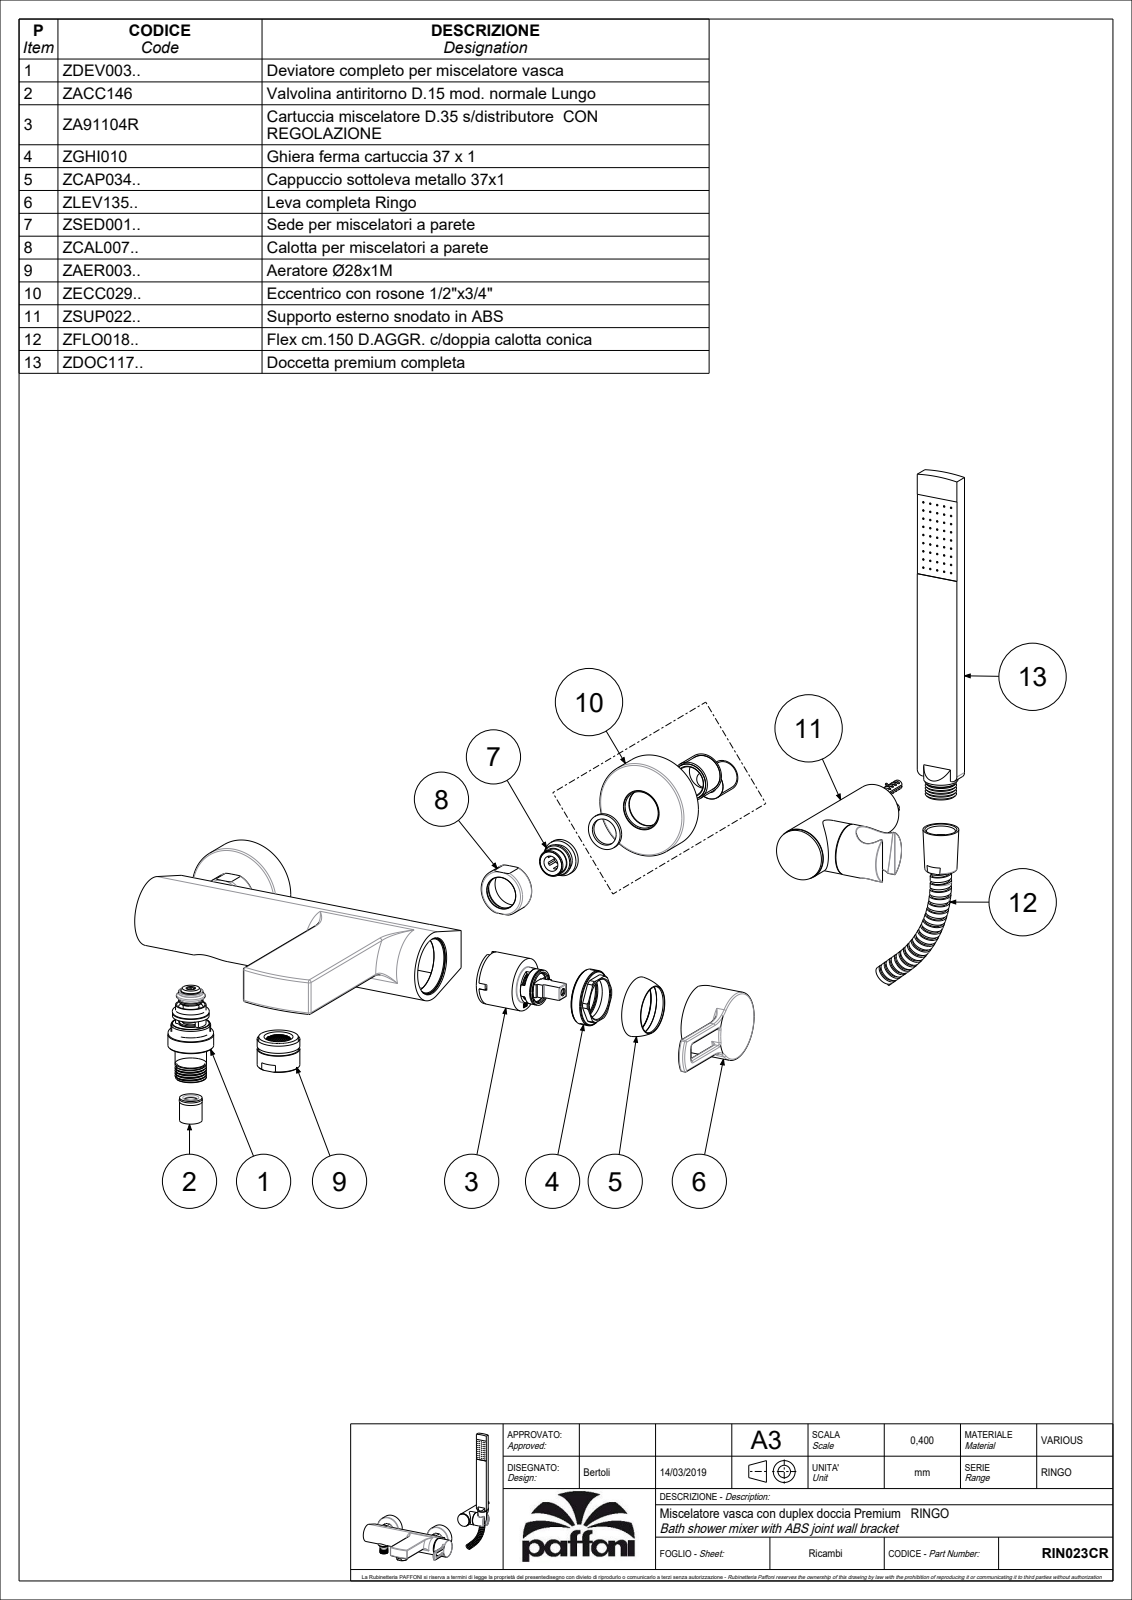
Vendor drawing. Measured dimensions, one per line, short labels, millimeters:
name: RIN023CR
written by: CREO PARAMETRIC BY PTC INC, 2020044 (CONFIG_CONTROL_DESIGN)
unit: mm
bodies: 7 solids, 3671 faces (2649 planar, 577 cylindrical, 445 other)
size: 385.7 × 364.5 × 195
volume: 468 678 mm³; area: 287 568 mm²
holes: 4× ⌀7, 3× ⌀20, 2× ⌀3.5, 2× ⌀4, 2× ⌀7.8, 2× ⌀9.5, 2× ⌀10.5, 2× ⌀12.7, 2× ⌀16, 2× ⌀18, 2× ⌀21, 2× ⌀21.6
bosses: 11× ⌀2, 3× ⌀27, 3× ⌀24, 3× ⌀6.9, 3× ⌀3.9, 2× ⌀63.5, 2× ⌀30, 2× ⌀28
rounds: 34× R0.5, 14× R0.3, 14× R1, 11× R0.15, 6× R1.5, 6× R2, 4× R5, 4× R5.2
face distances: 3.5, 3, 12, 20.5, 15, 22.5, 50.5, 10, 60.5, 5
hole spacings: 7.07, 8.6, 11.4, 150, 1.17, 4, 6, 6.21
